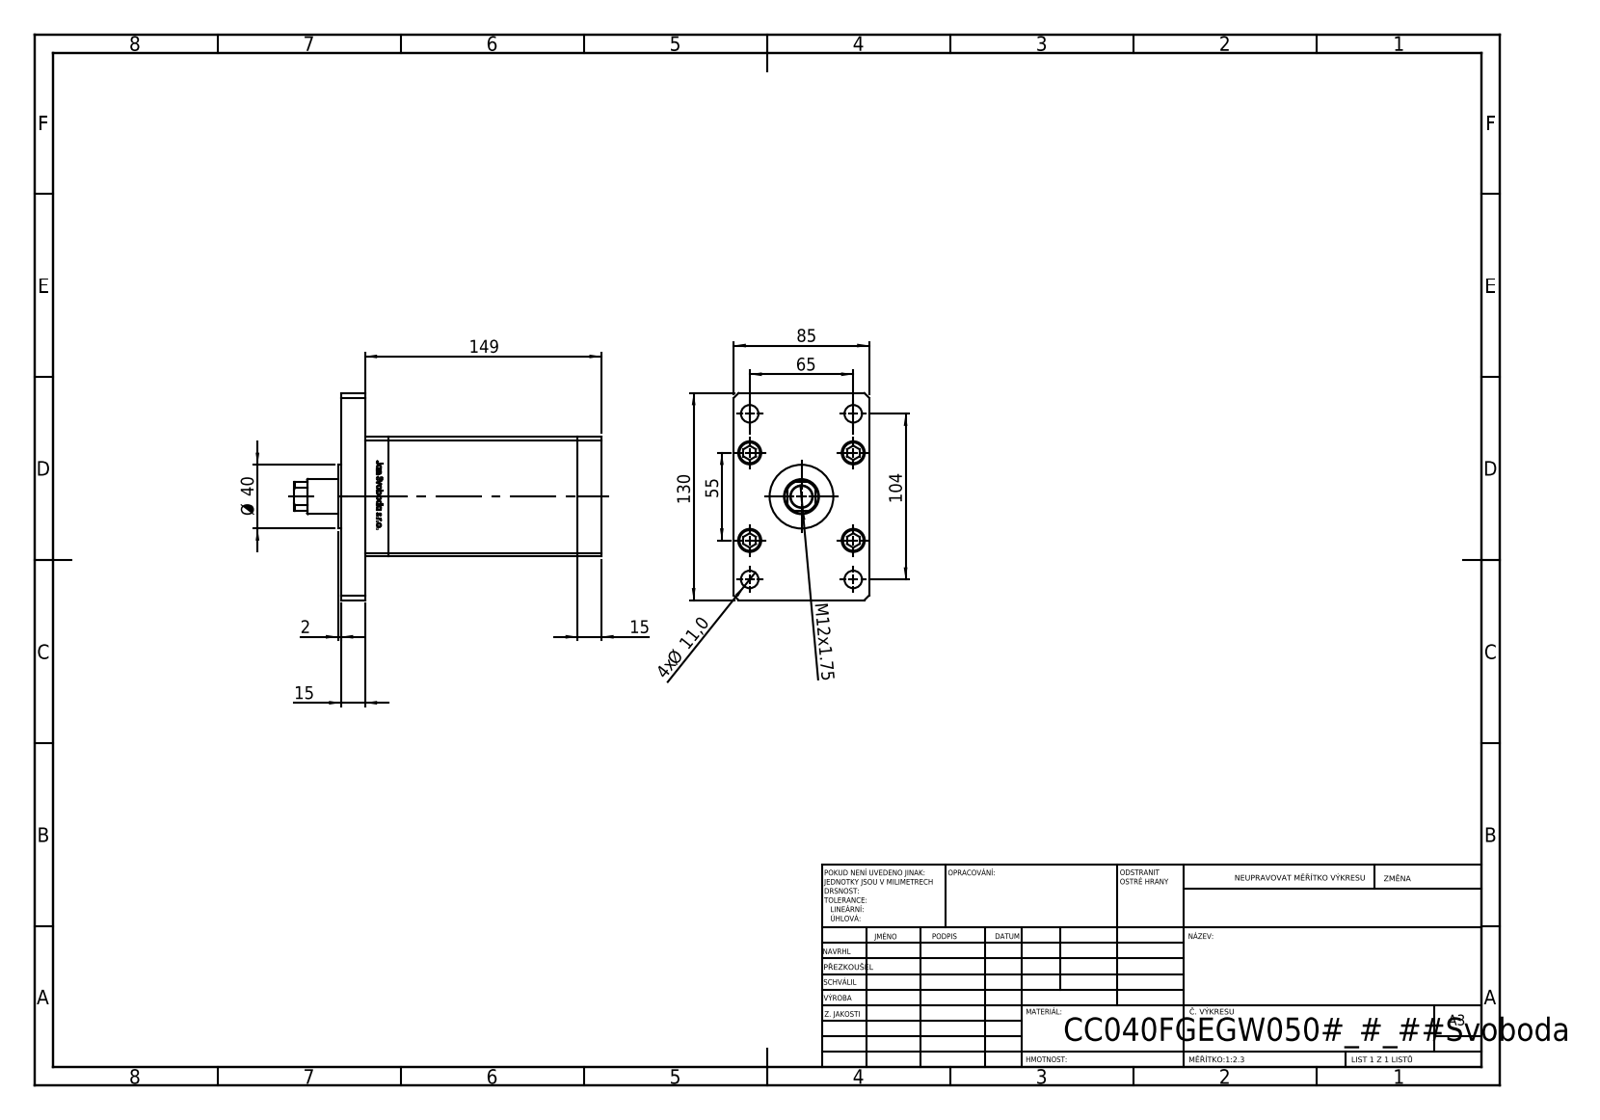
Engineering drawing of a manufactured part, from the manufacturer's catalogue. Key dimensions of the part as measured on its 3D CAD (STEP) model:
Part name (STEP PRODUCT): V220C_FRONT_F; V220C BACK_F; V220C_F; V220C_VC_F (+2 more)
STEP written by: SolidWorks 2019 (CONFIG_CONTROL_DESIGN)
Units: millimetres
Bodies: 19 solids, 1310 faces (517 planar, 187 cylindrical, 606 other)
Overall size (bounding box): 192.8 × 130 × 85
Volume: 1 002 000 mm³ · Surface area: 183 822 mm²
Round holes (diameter × count): ⌀11 ×9, ⌀15.5 ×5, ⌀10 ×4, ⌀14.5 ×4, ⌀2 ×2, ⌀13.16 ×2, ⌀13.5 ×1, ⌀22 ×1, ⌀23.5 ×1
Round bosses / shafts (diameter × count): ⌀8 ×9, ⌀14.5 ×5, ⌀40 ×1
Partial cylindrical surfaces — rounded edges, fillets, slot ends (radius × count): R0.93 ×2, R10.5 ×1
Main face-to-face distances: 15, 133.5, 148.5, 85, 30, 75, 118.5, 163.5, 10.5, 110.7
Hole centre spacings: 28, 24.5, 42.57, 61.32, 65, 69.46, 79.5, 102.69
